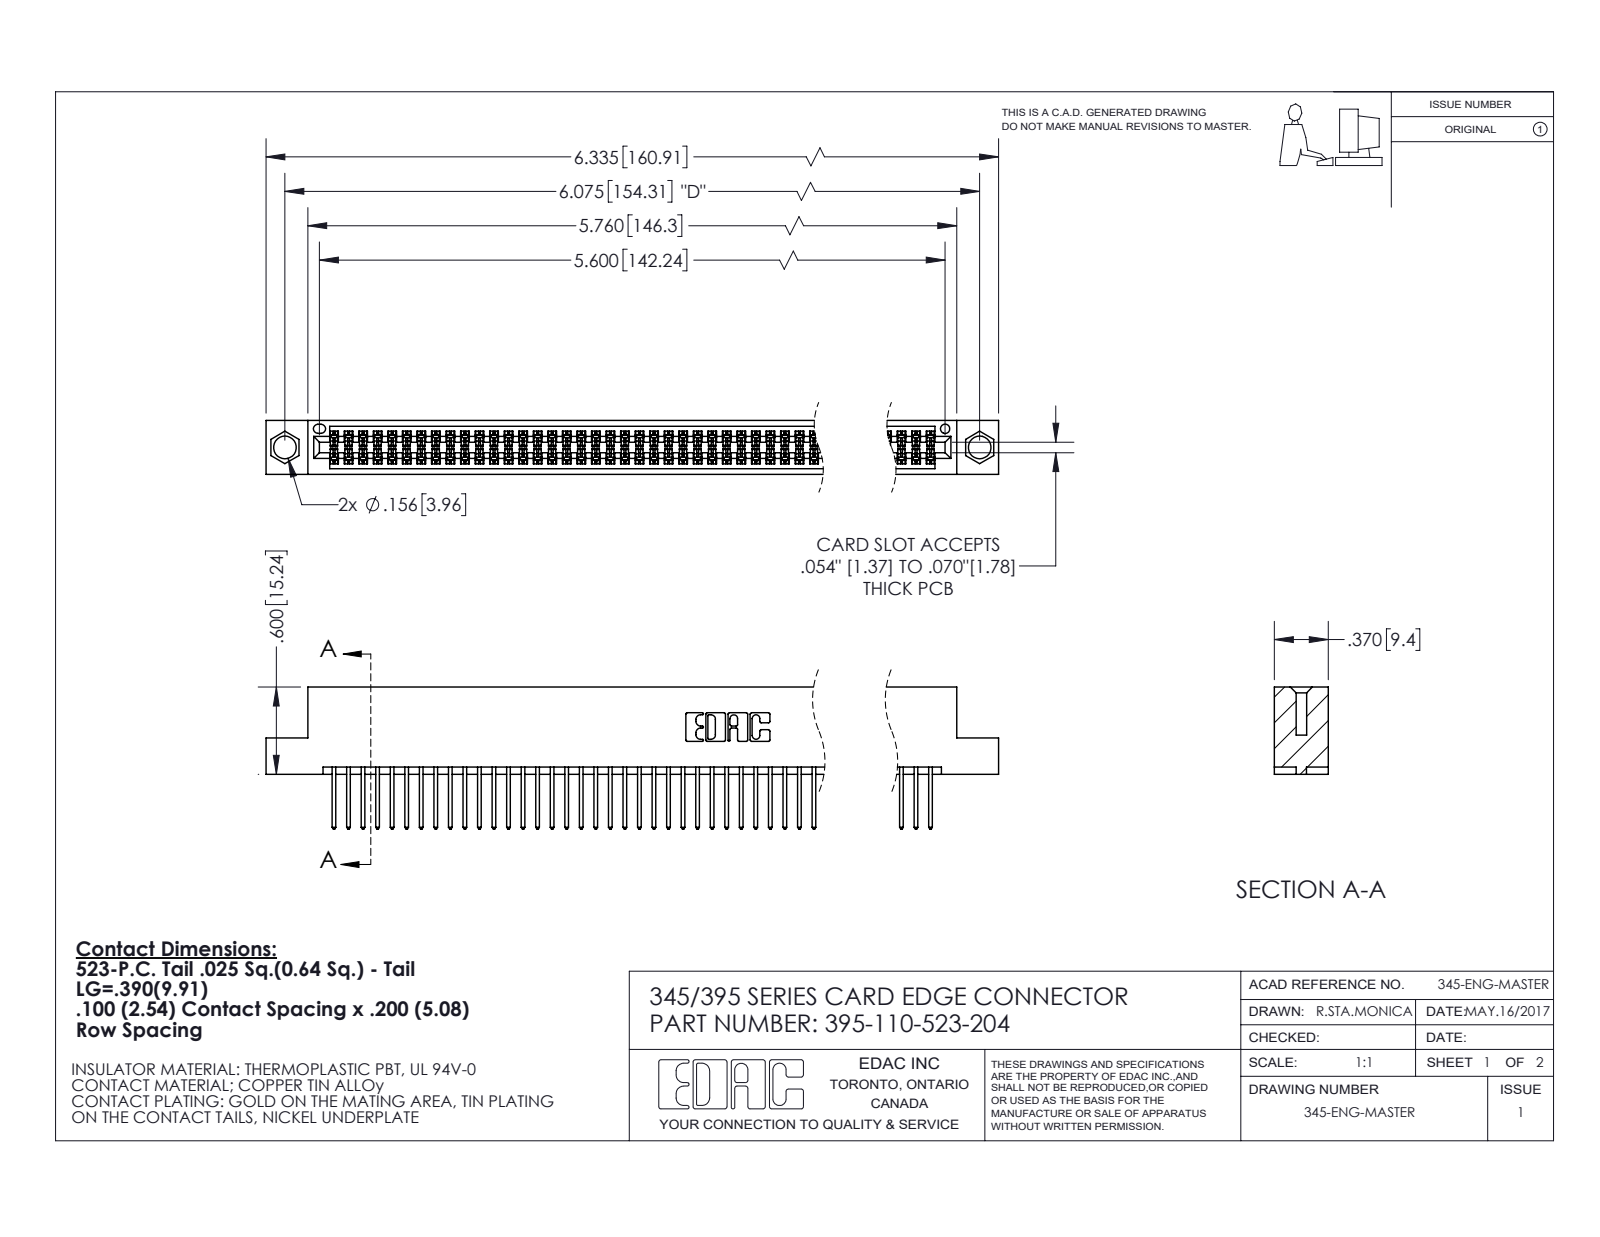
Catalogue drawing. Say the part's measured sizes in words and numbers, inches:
The part is named "395-110-523-204; 345 Part_Flush Mounting Lugs - 0.156 Dia-TI; 345-292-001_345-293-123". Its 3-D file was written by "SolidWorks 2020 (CONFIG_CONTROL_DESIGN)". It is 111 solids with 5640 faces: 3724 planar, 1916 cylindrical and 0 other. Overall it measures 6.335 by 0.977 by 0.37 inches. Its volume is 0.969 cubic inches and its surface area 38.09 square inches. Round holes: 2 of diameter 0.156, 1 of diameter 0.064. Partial cylindrical surfaces (rounded edges, fillets, slot ends): 165 of radius 0.006, 110 of radius 0.01, 22 of radius 0.01, 6 of radius 0.007, 6 of radius 0.031, 3 of radius 0.026, 2 of radius 0.014, 2 of radius 0.019. The main face-to-face distances are 0.298, 0.072, 0.2, 0.098, 0.272, 0.025, 0.37, 0.225, 0.175, 0.149. The hole center spacings are 0.27, 5.839, 6.075.
